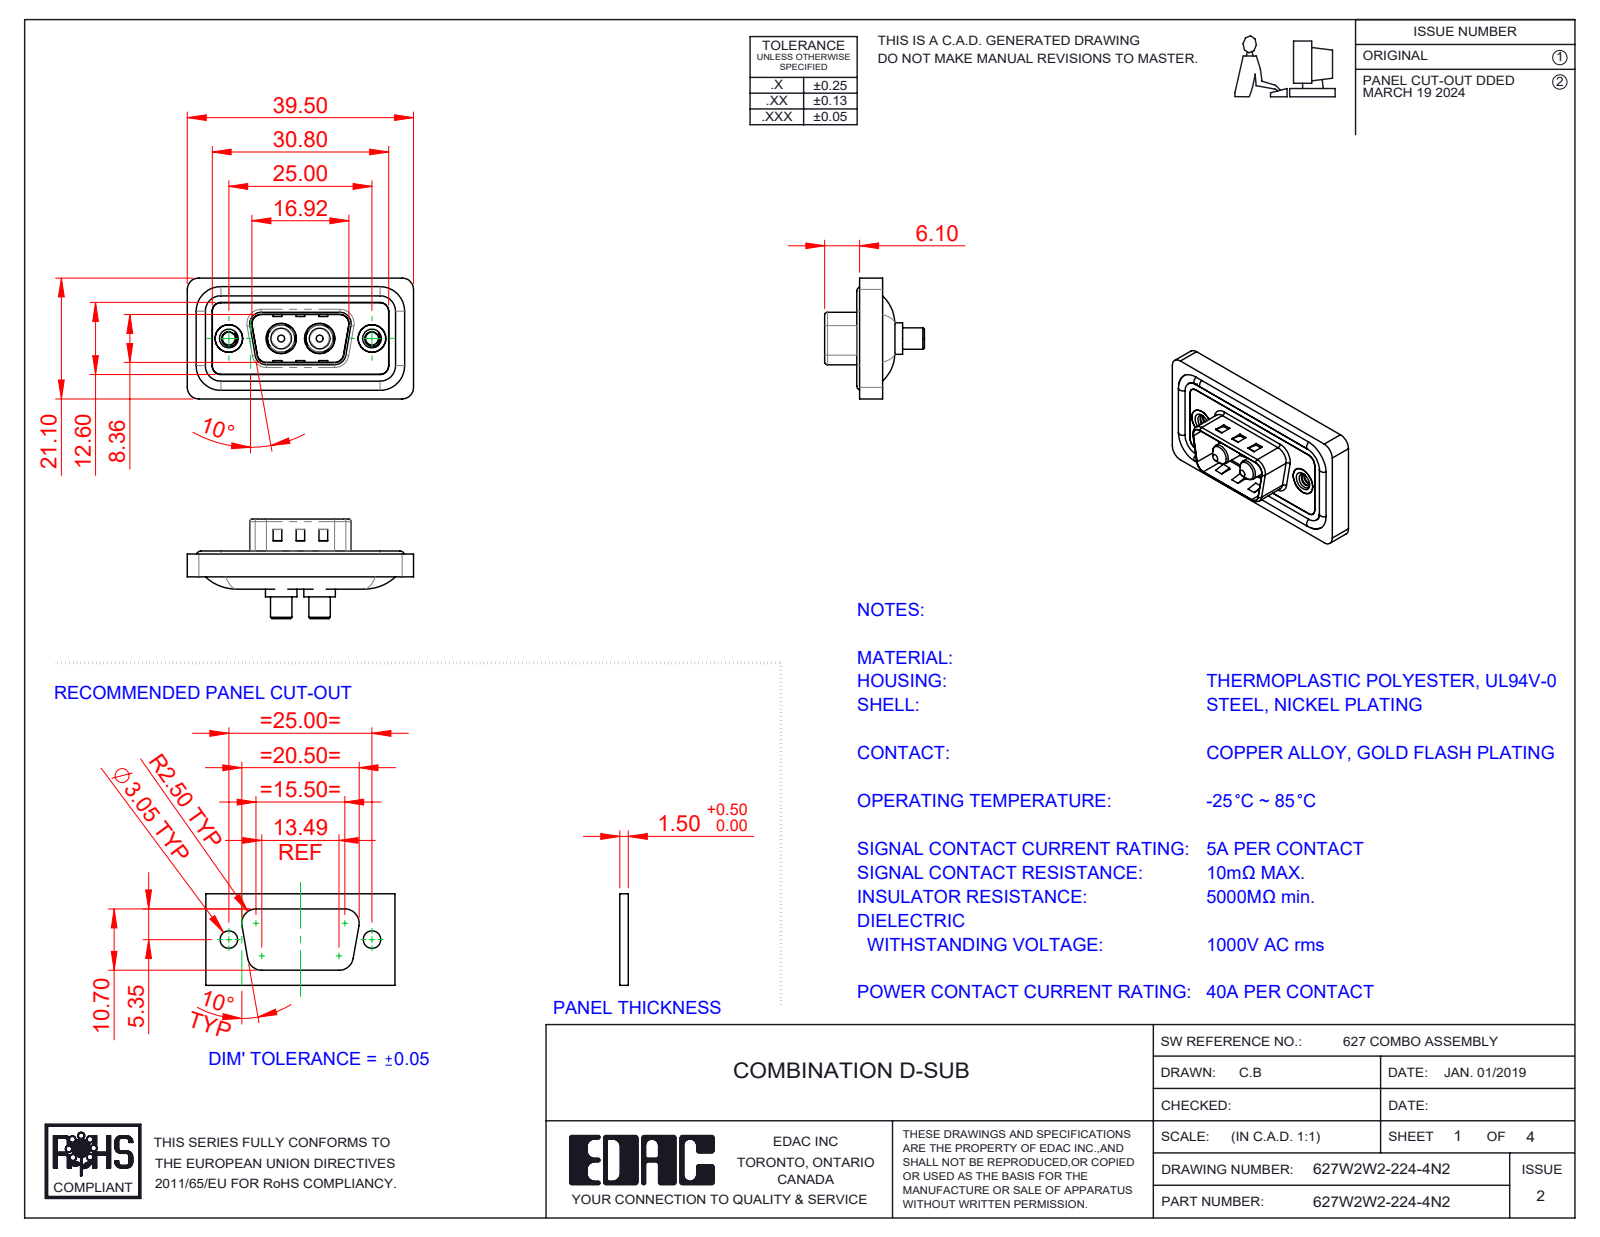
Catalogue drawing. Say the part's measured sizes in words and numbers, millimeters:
The part is named "Power Pin_40A S; 627W2W2-224-4N2; 627Combo Housing_2W2; 627Combo Shell Front_09 Contacts (+3 more)". Its 3-D file was written by "SolidWorks 2023 (CONFIG_CONTROL_DESIGN)". It is 11 solids with 489 faces: 165 planar, 218 cylindrical and 106 other. Overall it measures 39.5 by 21.1 by 17.4 millimeters. Its volume is 4 497 cubic millimeters and its surface area 7 006 square millimeters. Round holes: 2 of diameter 2.26, 2 of diameter 4, 2 of diameter 4.8, 2 of diameter 4.85, 2 of diameter 5, 2 of diameter 5.3. Round bosses or shafts: 4 of diameter 1.6, 2 of diameter 5.5, 2 of diameter 5.2, 2 of diameter 4.9, 2 of diameter 4.75, 2 of diameter 3.75, 2 of diameter 3.6. Partial cylindrical surfaces (rounded edges, fillets, slot ends): 22 of radius 1.5, 18 of radius 2, 8 of radius 0.5, 8 of radius 1.6, 4 of radius 0.25, 4 of radius 0.6, 4 of radius 0.65, 4 of radius 0.9. The main face-to-face distances are 0.4, 1.1, 2.9, 3.1, 0.5, 1.6, 1.5, 2.5, 4, 0.7. The hole center spacings are 9.14, 15.86, 6.72, 25.
